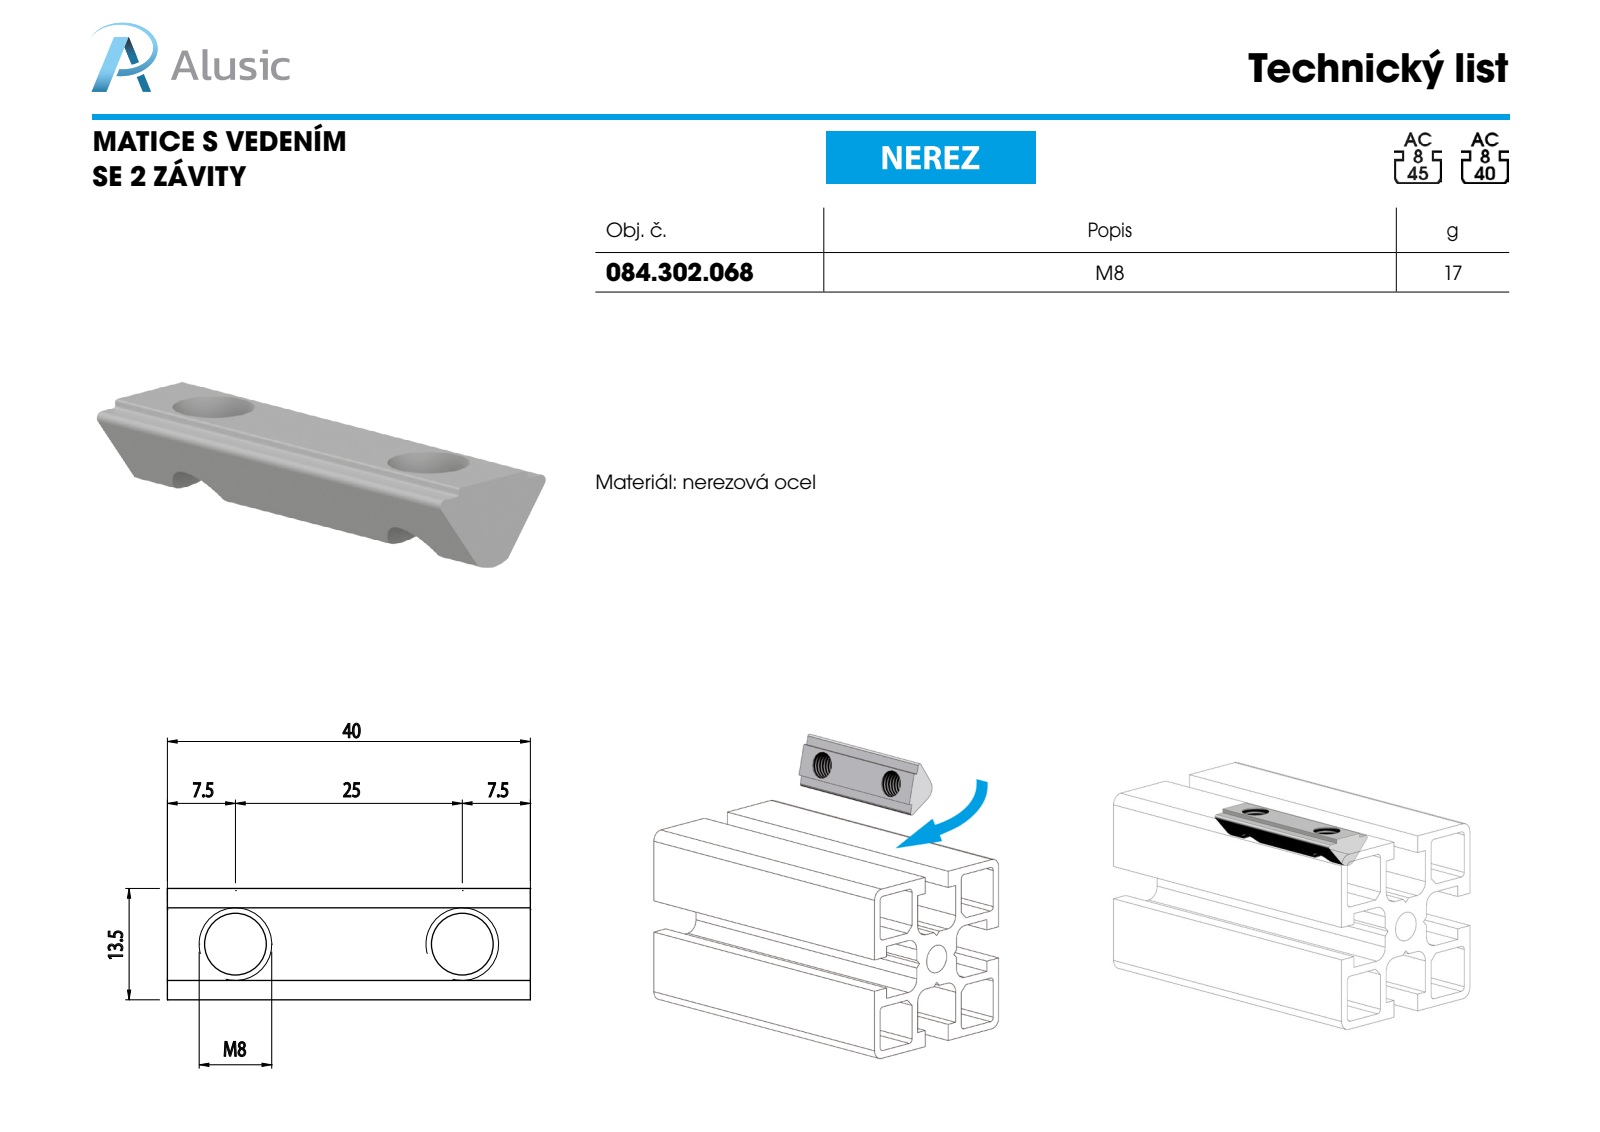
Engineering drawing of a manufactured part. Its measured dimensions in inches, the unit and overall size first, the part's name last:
Units: inches
Overall size (bounding box): 1.575 × 0.483 × 0.295
Round holes (diameter × count): ⌀0.268 ×2
Partial cylindrical surfaces — rounded edges, fillets, slot ends (radius × count): R0.008 ×4, R0.02 ×2, R0.148 ×1
Main face-to-face distances: 0.028, 1.575, 0.315
Hole centre spacings: 0.984
Volume: 0.115 in³ · Surface area: 2.342 in²
Bodies: 1 solid, 23 faces (9 planar, 14 cylindrical, 0 other)
Part name (STEP PRODUCT): 084.302.068
STEP written by: SolidWorks 2012 (CONFIG_CONTROL_DESIGN)
